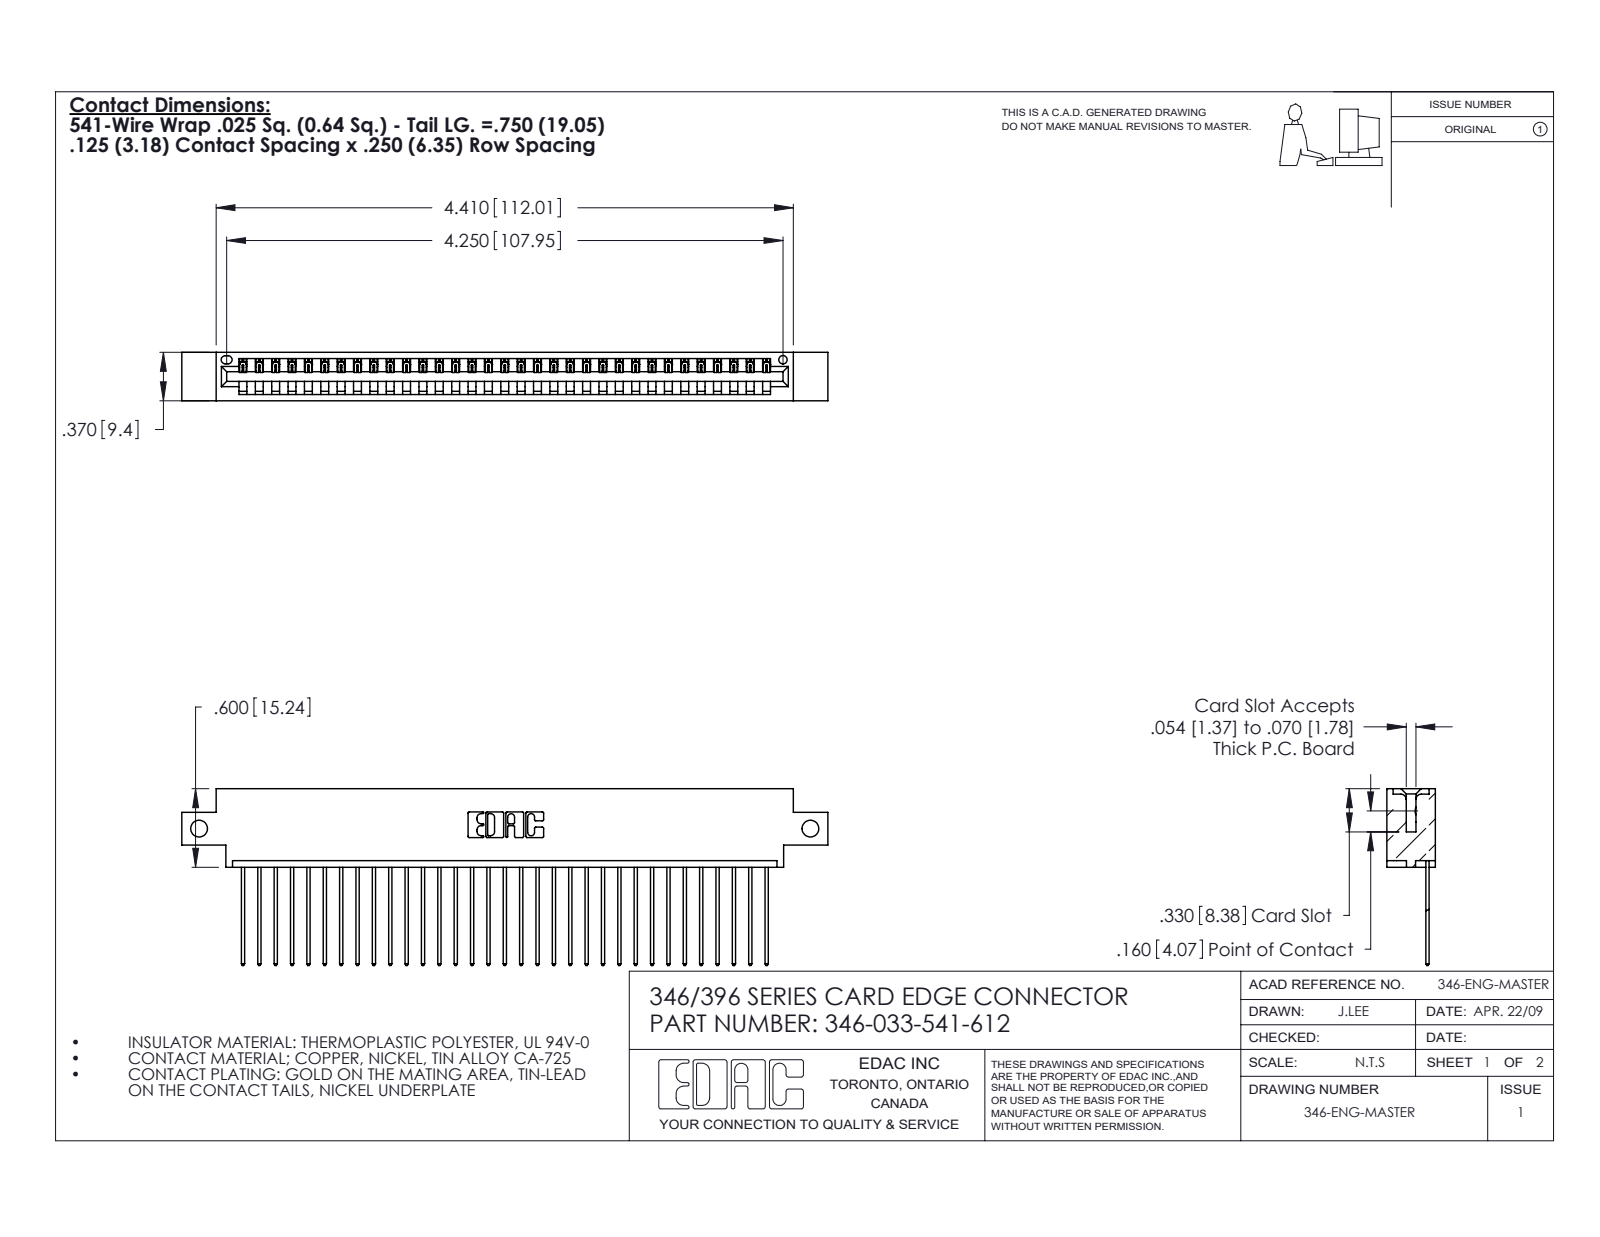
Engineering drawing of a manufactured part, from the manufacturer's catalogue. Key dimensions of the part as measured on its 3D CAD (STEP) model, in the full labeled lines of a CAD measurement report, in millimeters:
Part name (STEP PRODUCT): 346-033-541-612; 345-292-001_345-293-141; 346 Part_0.170 Offset - Side Mount
STEP written by: SolidWorks 2020 (CONFIG_CONTROL_DESIGN)
Units: millimetres
Bodies: 34 solids, 2040 faces (1400 planar, 640 cylindrical, 0 other)
Overall size (bounding box): 125.3 × 34.3 × 9.4
Volume: 11 800 mm³ · Surface area: 15 320 mm²
Round holes (diameter × count): ⌀3.3 ×2, ⌀1.6 ×1
Partial cylindrical surfaces — rounded edges, fillets, slot ends (radius × count): R0.2 ×66, R0.3 ×66, R0.3 ×22, R0.2 ×6, R0.8 ×6, R0.7 ×3, R0.8 ×2, R1 ×2
Main face-to-face distances: 1.2, 8.2, 9.4, 6.4, 1.8, 7.6, 0.6, 3.8, 5.6, 2.5
Hole centre spacings: 118.6
